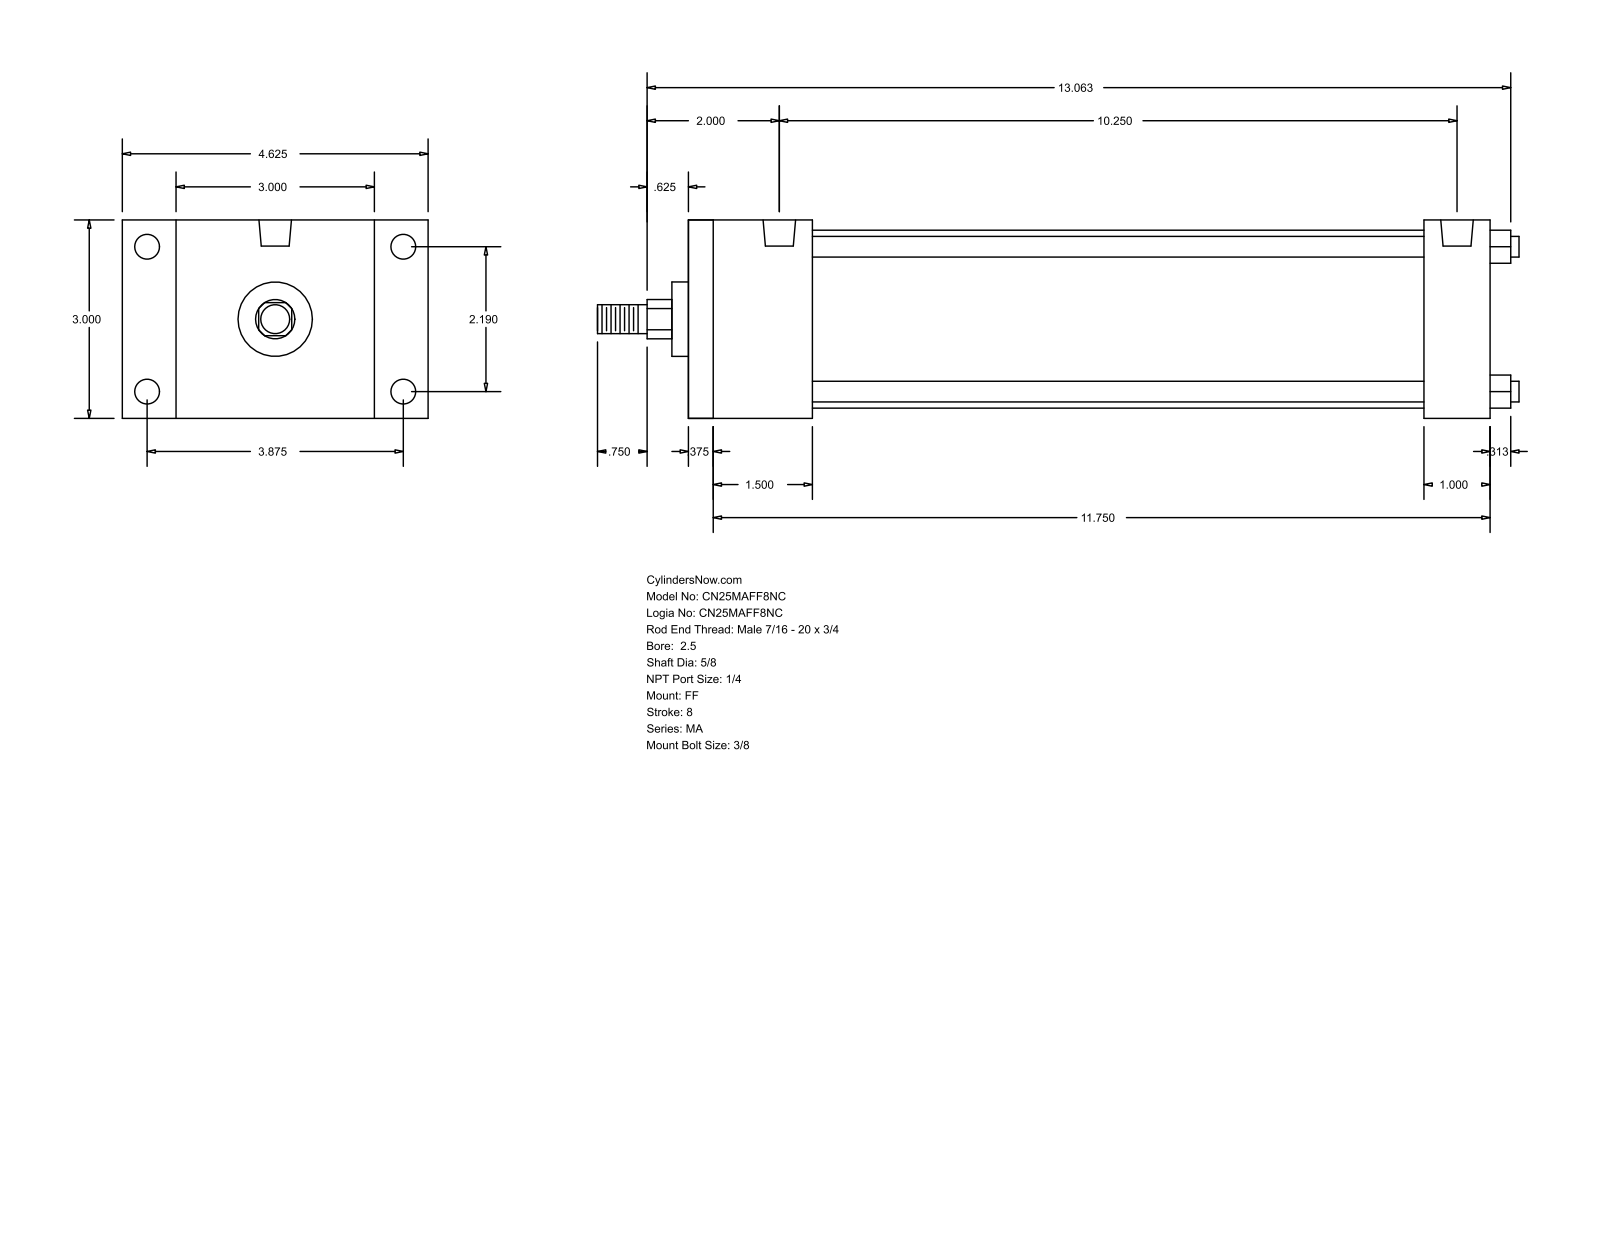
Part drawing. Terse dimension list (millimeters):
name: MA_FF__0250_0.625
written by: GSSL Pune (CONFIG_CONTROL_DESIGN)
unit: mm
bodies: 0 solids, 92 faces (64 planar, 28 cylindrical, 0 other)
size: 354.01 × 117.47 × 76.2
holes: 4× ⌀7.94, 4× ⌀9.53, 2× ⌀12.49
bosses: 4× ⌀7.94, 1× ⌀68.33, 1× ⌀28.57, 1× ⌀15.88, 1× ⌀11.11
rounds: 1× R7.54
face distances: 76.2, 307.97, 298.45, 9.52, 25.4, 47.62, 282.57, 38.1, 273.05, 234.95
hole spacings: 55.62, 98.42, 113.05, 260.35
